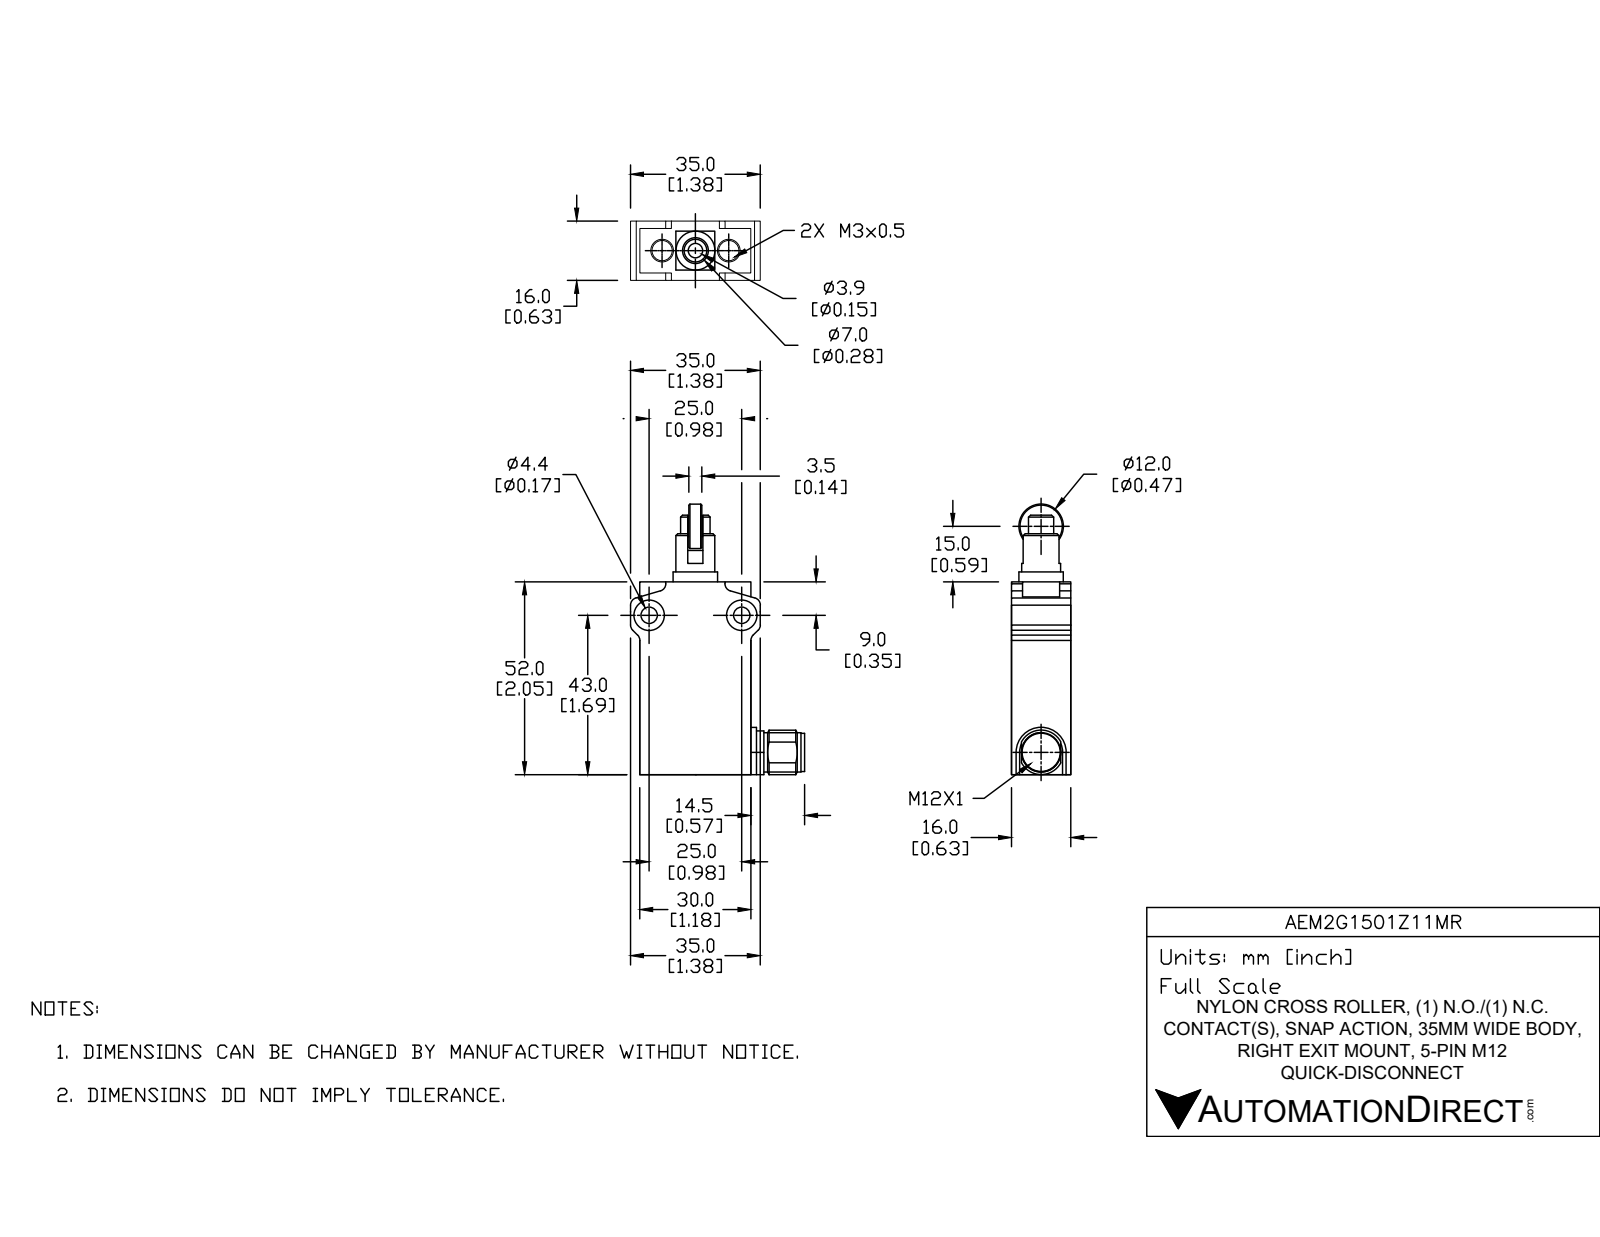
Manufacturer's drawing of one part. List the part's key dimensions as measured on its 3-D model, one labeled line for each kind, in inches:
Part name (STEP PRODUCT): AEM2G1501Z11MR
STEP written by: SolidWorks 2019 (AUTOMOTIVE_DESIGN)
Units: inches
Bodies: 5 solids, 157 faces (68 planar, 51 cylindrical, 38 other)
Overall size (bounding box): 2.878 × 1.831 × 0.63
Volume: 1.644 in³ · Surface area: 14.91 in²
Round holes (diameter × count): ⌀0.118 ×2, ⌀0.173 ×2, ⌀0.323 ×2, ⌀0.317 ×1
Round bosses / shafts (diameter × count): ⌀0.472 ×3, ⌀0.417 ×1, ⌀0.413 ×1, ⌀0.406 ×1, ⌀0.313 ×1, ⌀0.22 ×1
Partial cylindrical surfaces — rounded edges, fillets, slot ends (radius × count): R0.079 ×8, R0.256 ×1
Main face-to-face distances: 0.63, 1.181, 2.047, 0.472, 0.157, 0.15, 0.51, 0.671, 0.098, 0.608
Hole centre spacings: 0.374, 0.748, 0.984
